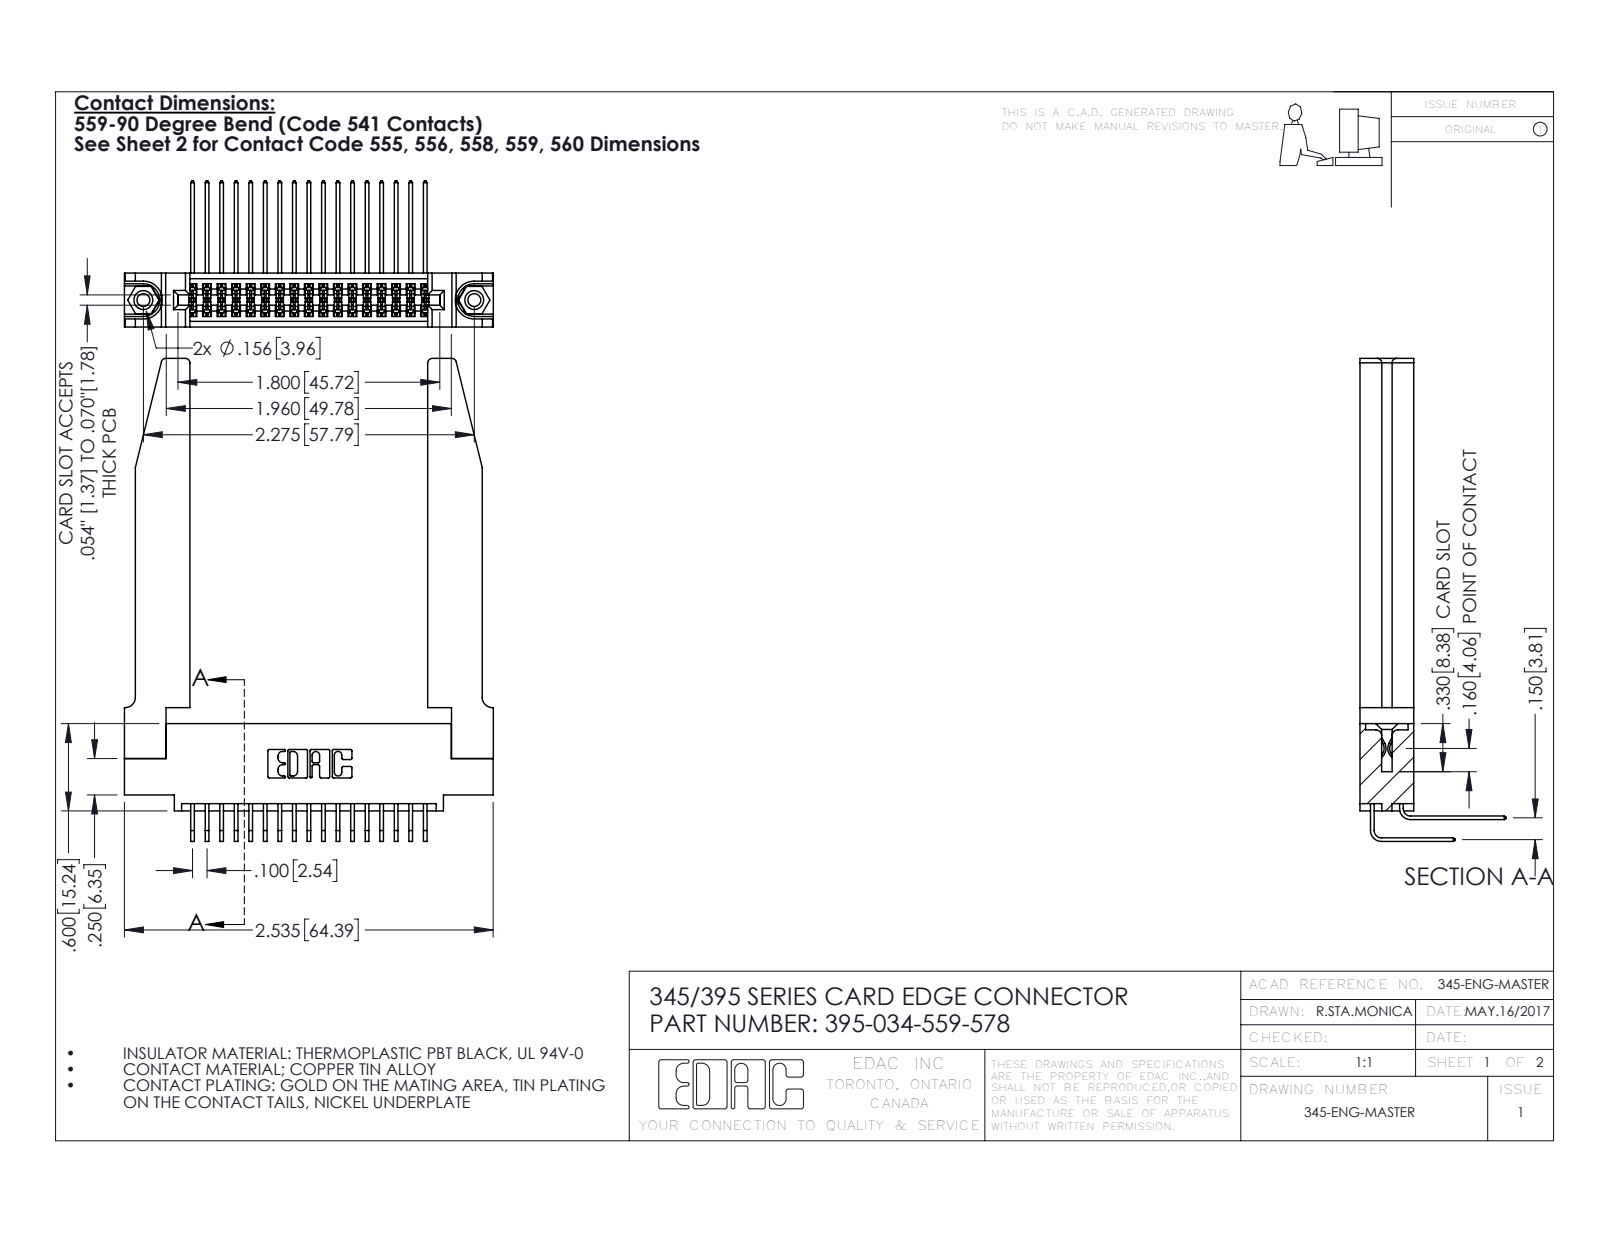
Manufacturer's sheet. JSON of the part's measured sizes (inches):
{"part_name": "345-250-001_345-250-001-102; 395-034-559-578; 345-292-001_558 559 Tail - 1; 345-292-001_559 Tail - 2 (+2 more)", "step_written_by": "SolidWorks 2016 (CONFIG_CONTROL_DESIGN)", "units": "inches", "bodies": {"solids": 39, "faces": 2132, "planar": 1416, "cylindrical": 664, "other": 52}, "overall_size": [3.319, 2.536, 1.005], "volume_in3": 0.849, "surface_area_in2": 25.51, "round_holes": [[0.089, 2], [0.125, 2], [0.156, 2], [0.064, 1]], "round_bosses_or_shafts": [[0.155, 2]], "partial_cylinders_radius": [[0.006, 52], [0.01, 22], [0.03, 8], [0.007, 6], [0.031, 6], [0.026, 3], [0.014, 2], [0.019, 2]], "face_to_face_distances": [0.37, 0.072, 0.298, 0.2, 0.098, 0.272, 0.025, 0.148, 0.15, 0.225], "hole_center_spacings": [0.27, 2.041, 2.275]}
